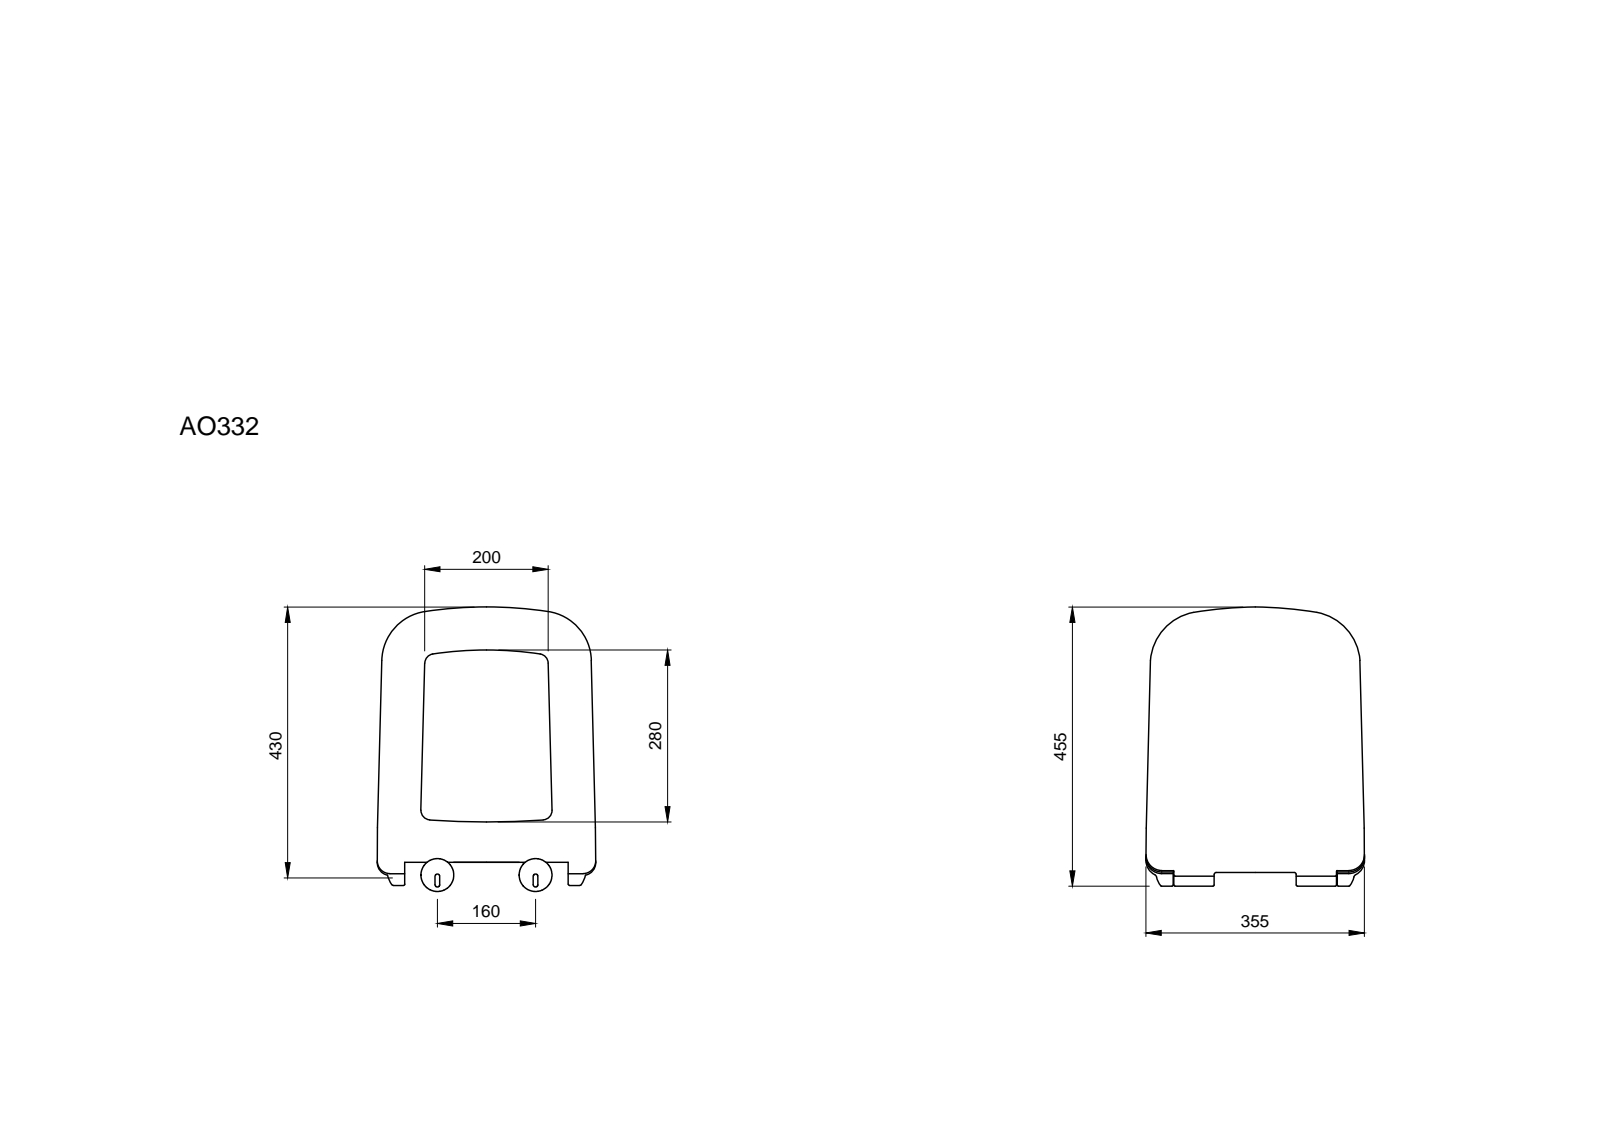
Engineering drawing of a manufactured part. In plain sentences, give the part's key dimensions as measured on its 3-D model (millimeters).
The part is named "Dell644C4053rcy2". Its 3-D file was written by "SIEMENS PLM Software NX 11.0 (AUTOMOTIVE_DESIGN)". It is 2 solids with 318 faces: 37 planar, 65 cylindrical and 216 other. Overall it measures 485.44 by 470.52 by 359.69 millimeters. Its volume is 1 934 000 cubic millimeters and its surface area 558 382 square millimeters. Round bosses or shafts: 1 of diameter 33. Partial cylindrical surfaces (rounded edges, fillets, slot ends): 13 of radius 1, 4 of radius 85, 2 of radius 1.5, 2 of radius 2, 2 of radius 14.8, 2 of radius 15, 2 of radius 19.8, 2 of radius 20. The main face-to-face distances are 5.01, 65.17, 70.18, 20.64, 283.36, 19.64, 284.36, 1, 263.72, 262.72.
